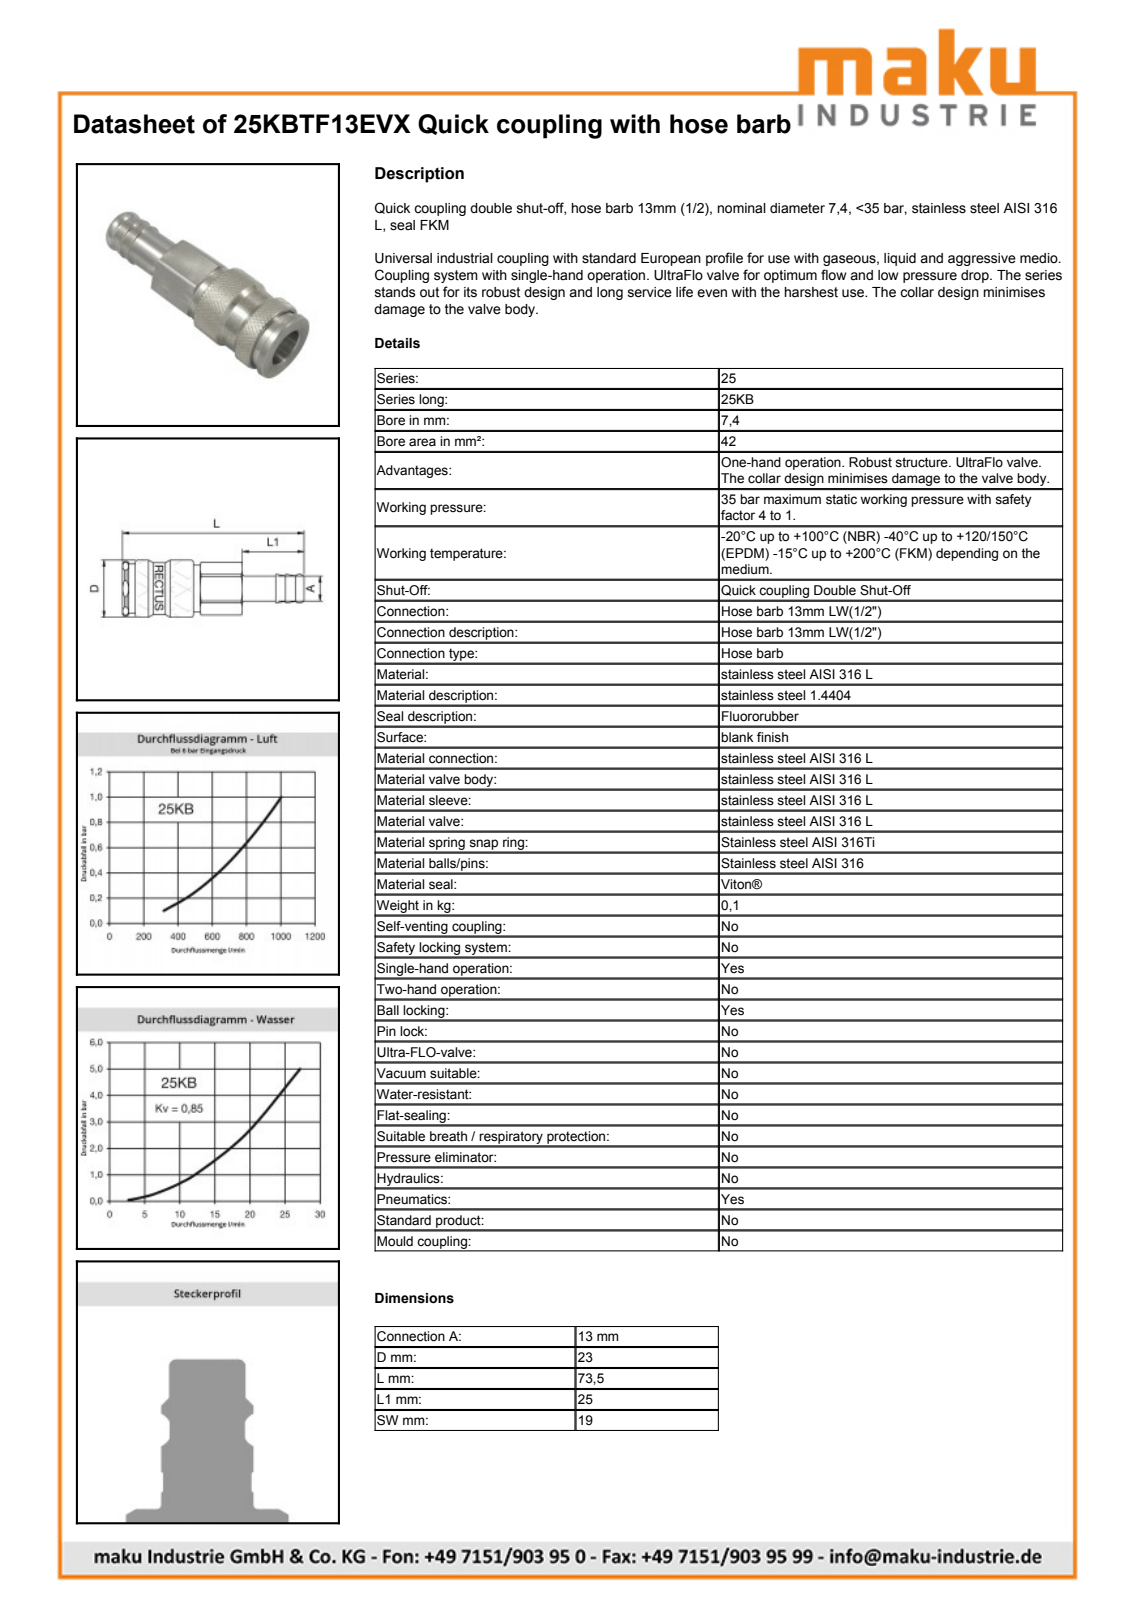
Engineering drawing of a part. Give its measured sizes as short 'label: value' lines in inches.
name: D108097
written by: Autodesk Inventor 2013 (AUTOMOTIVE_DESIGN)
unit: in
bodies: 2 solids, 613 faces (242 planar, 85 cylindrical, 286 other)
size: 2.894 × 0.911 × 0.911
volume: 1.185 in³; area: 16.52 in²
holes: 1× ⌀0.433, 1× ⌀0.594, 1× ⌀0.63, 1× ⌀0.679, 1× ⌀0.762, 1× ⌀0.789
bosses: 1× ⌀0.911, 1× ⌀0.866, 1× ⌀0.827, 1× ⌀0.787, 1× ⌀0.746, 1× ⌀0.602, 1× ⌀0.591, 1× ⌀0.583
rounds: 1× R0.409, 1× R0.421
face distances: 0.748, 2.894, 1.909, 0.984, 0.965, 0.945, 1.929, 0.207, 0.758, 1.132
